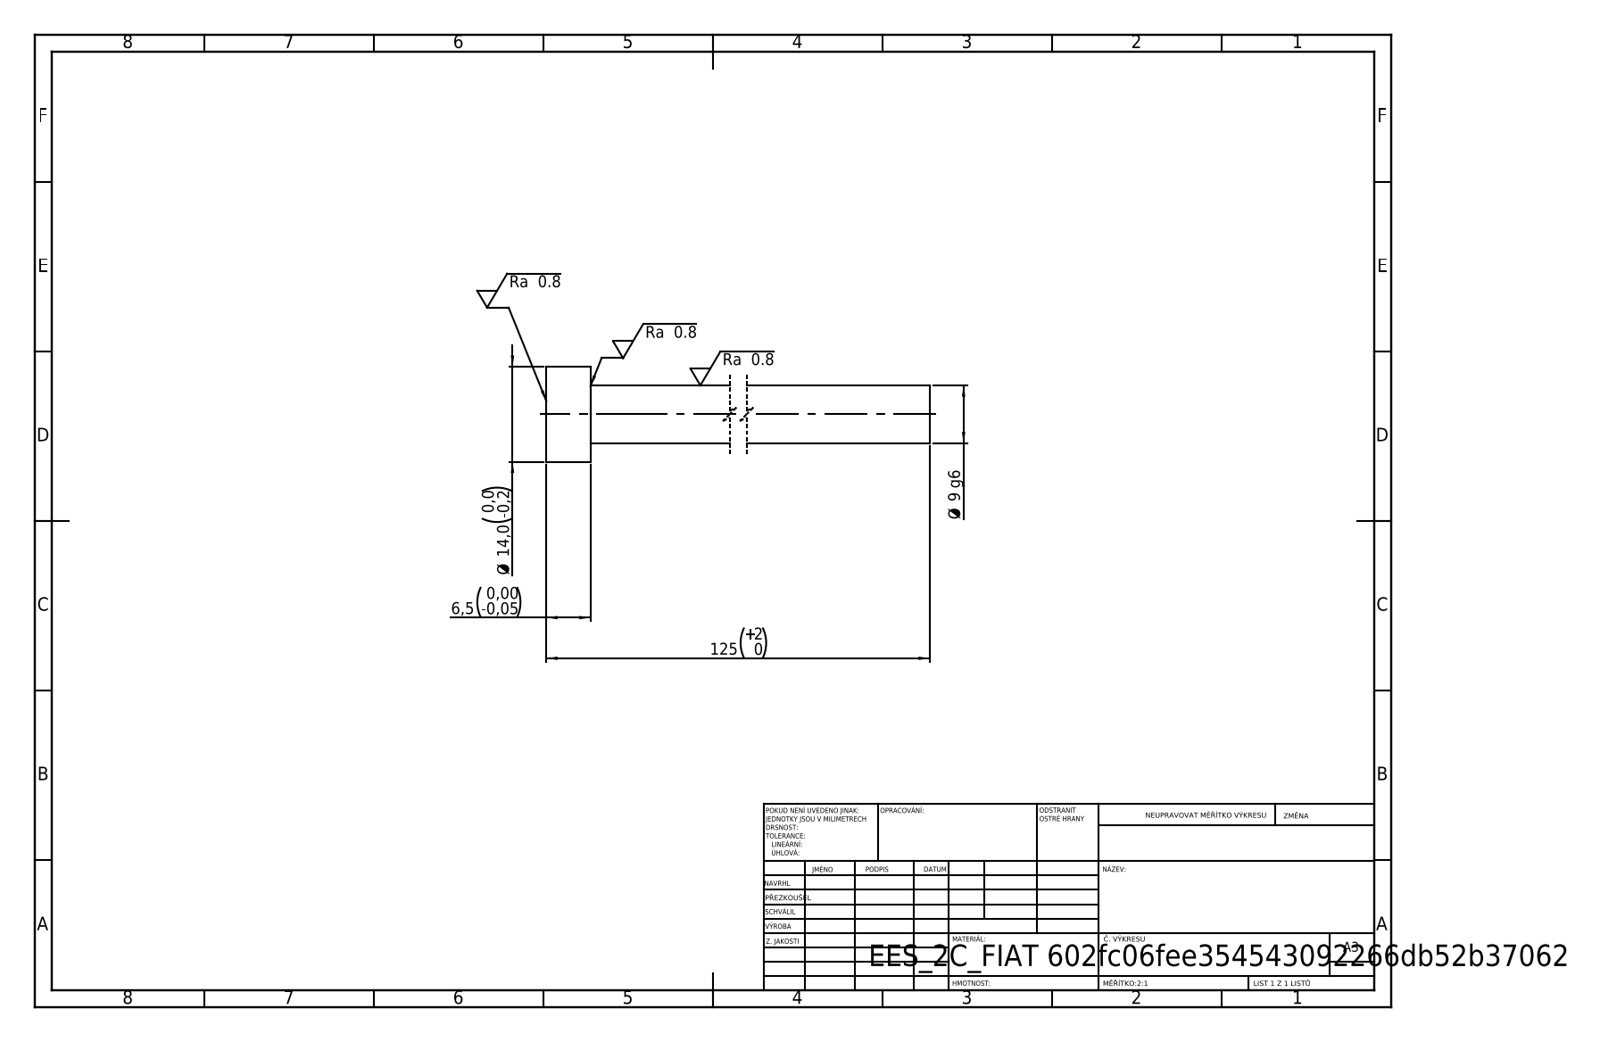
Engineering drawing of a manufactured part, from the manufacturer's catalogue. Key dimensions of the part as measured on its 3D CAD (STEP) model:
STEP written by: SolidWorks 2019 (CONFIG_CONTROL_DESIGN)
Units: millimetres
Bodies: 1 solid, 7 faces (3 planar, 4 cylindrical, 0 other)
Overall size (bounding box): 125 × 14 × 14
Volume: 7 725 mm³ · Surface area: 3 758 mm²
Round bosses / shafts (diameter × count): ⌀14 ×1, ⌀8.5 ×1
Main face-to-face distances: 6.5, 125, 118.5
